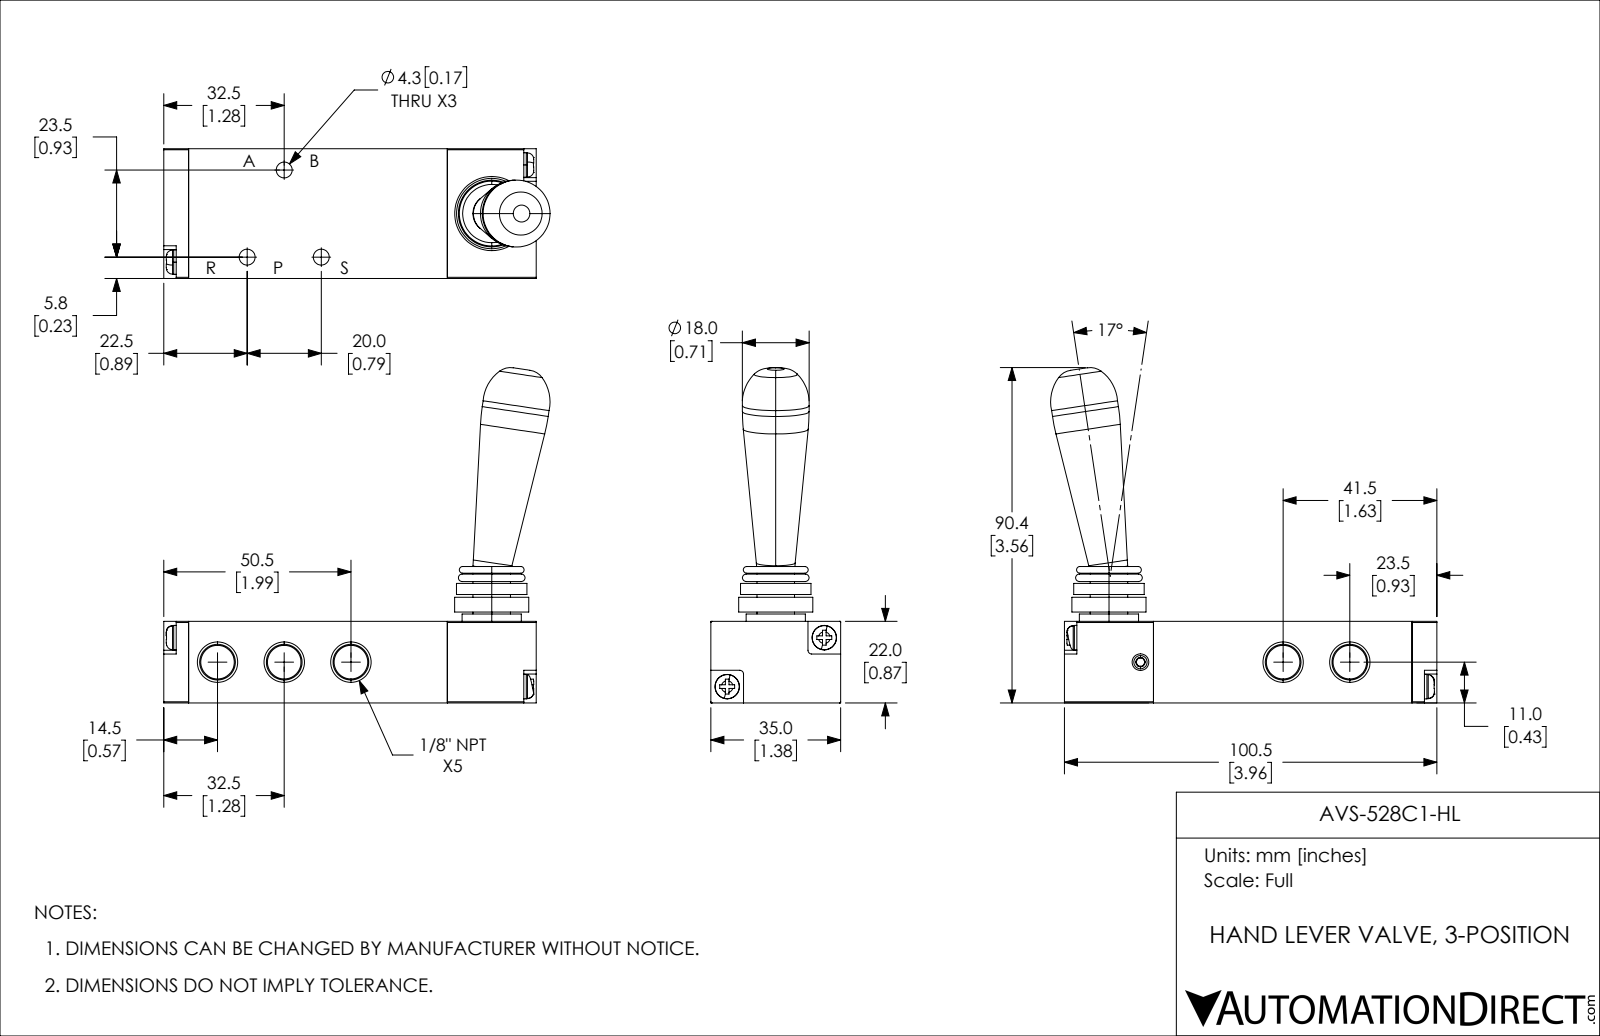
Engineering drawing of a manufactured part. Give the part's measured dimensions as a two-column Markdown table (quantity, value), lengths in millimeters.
| quantity | value |
| --- | --- |
| part name | AVS-528C1-HL |
| STEP written by | SolidWorks 2018 (AUTOMOTIVE_DESIGN) |
| units | millimeters |
| bodies | 4 solids, 231 faces (130 planar, 57 cylindrical, 44 other) |
| overall size | 104.24 × 90.45 × 35 |
| volume | 84 715 mm³ |
| surface area | 23 988 mm² |
| round holes (diameter × count) | 4.3 × 3, 4.5 × 1, 16 × 1 |
| round bosses / shafts (diameter × count) | 6.6 × 4, 6.5 × 4, 20 × 1, 19 × 1, 18 × 1, 10.13 × 1, 3.6 × 1 |
| partial cylindrical surfaces (radius × count) | 0.3 × 4, 1 × 4 |
| main face-to-face distances | 22, 35, 69.8, 24, 93.8, 2, 6.7, 100.5, 76.5, 4 |
| hole center spacings | 25.54, 20, 47.48, 57.22, 67.04 |
